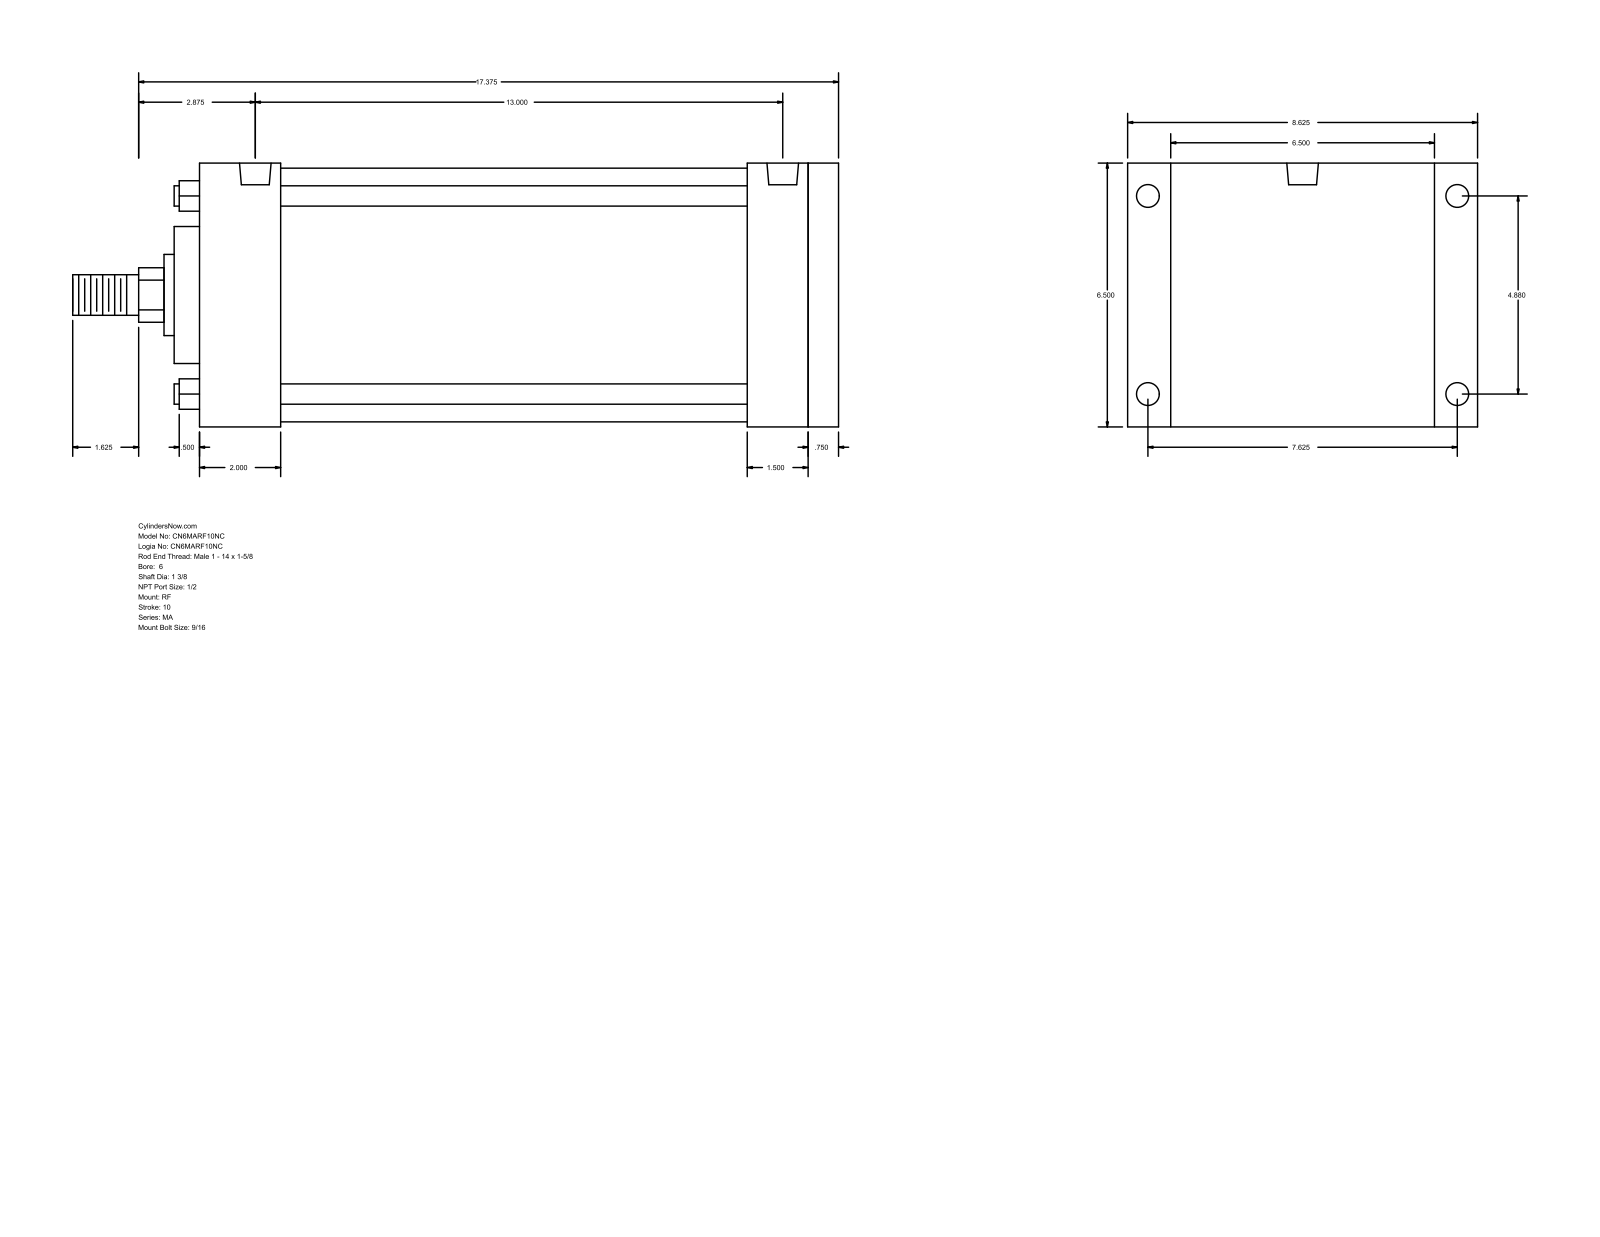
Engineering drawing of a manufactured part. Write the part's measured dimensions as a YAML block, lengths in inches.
part_name: "MA_RF__0600_1.375"
step_written_by: "GSSL Pune (CONFIG_CONTROL_DESIGN)"
units: inches
bodies: {solids: 0, faces: 94, planar: 65, cylindrical: 29, other: 0}
overall_size: [19, 8.625, 6.5]
round_holes:
  - {diameter: 0.563, count: 4}
  - {diameter: 0.687, count: 4}
  - {diameter: 0.778, count: 2}
round_bosses_or_shafts:
  - {diameter: 0.5, count: 4}
  - {diameter: 6.25, count: 1}
  - {diameter: 3.375, count: 1}
  - {diameter: 2, count: 1}
  - {diameter: 1.375, count: 1}
  - {diameter: 1, count: 1}
partial_cylinders:
  - {radius: 0.672, count: 1}
face_to_face_distances: [6.5, 15.875, 0.75, 15.125, 2, 13.125, 13.875, 13.625, 11.625, 1.5]
hole_center_spacings: [4.88, 7.625, 9.053, 13.125, 0.125, 13]
